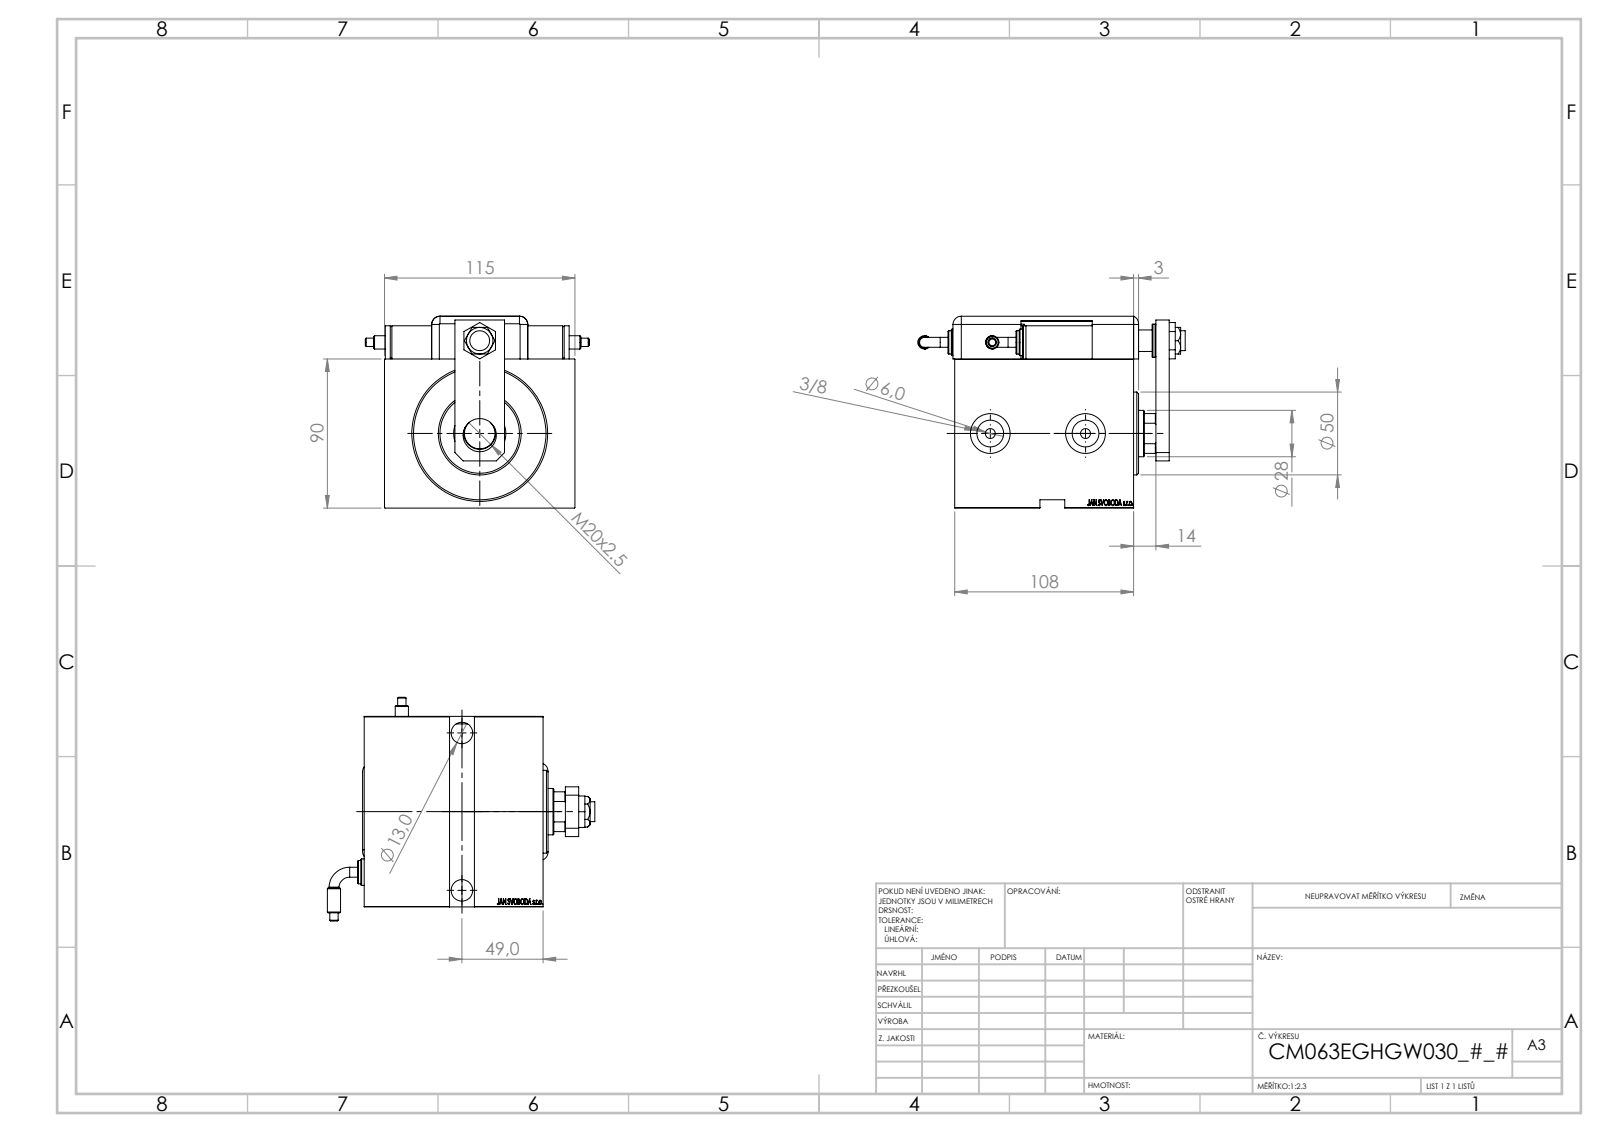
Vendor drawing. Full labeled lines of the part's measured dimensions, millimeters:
Part name (STEP PRODUCT): TYC; SWITCH_Q_FRONT_BACK; SWITCH DIM A_G; SWITCH Q (+7 more)
STEP written by: SolidWorks 2019 (CONFIG_CONTROL_DESIGN)
Units: millimetres
Bodies: 13 solids, 1262 faces (620 planar, 109 cylindrical, 533 other)
Overall size (bounding box): 161.46 × 135.01 × 115.8
Volume: 1 118 000 mm³ · Surface area: 185 801 mm²
Round holes (diameter × count): ⌀13 ×3, ⌀4 ×2, ⌀6 ×2, ⌀8 ×2, ⌀16.17 ×2, ⌀19 ×2, ⌀24 ×2, ⌀12 ×1, ⌀14 ×1, ⌀18.5 ×1, ⌀20 ×1, ⌀28 ×1
Round bosses / shafts (diameter × count): ⌀20 ×3, ⌀16 ×2, ⌀14 ×2, ⌀8 ×2, ⌀6 ×2, ⌀5.04 ×2, ⌀50 ×1
Partial cylindrical surfaces — rounded edges, fillets, slot ends (radius × count): R5 ×9, R10 ×1, R13.5 ×1
Main face-to-face distances: 108, 3, 90, 115, 19, 89, 115.8, 25.8, 5, 2.8
Hole centre spacings: 55.93, 70.91, 1, 20, 56, 57, 57.5, 95
